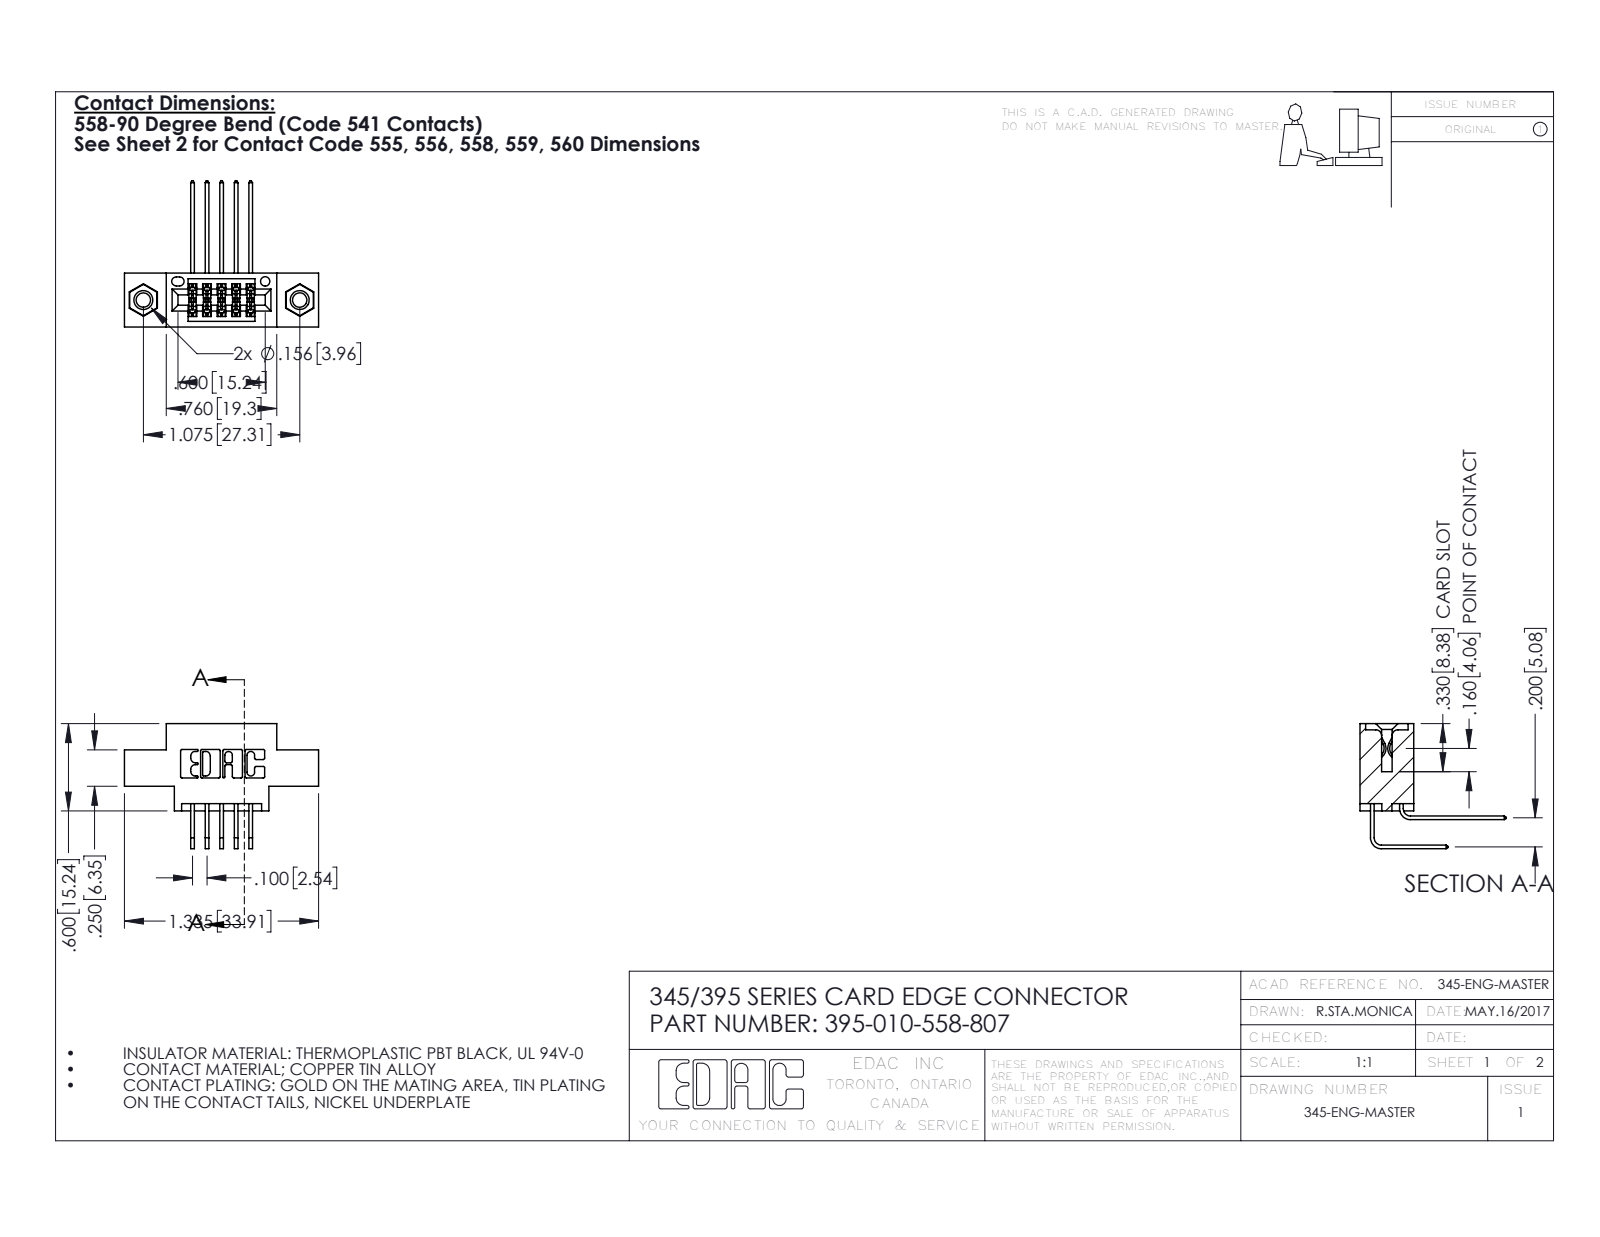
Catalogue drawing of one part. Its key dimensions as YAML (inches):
part_name: "345-292-001_558 559 Tail - 1; 345-292-001_558 Tail - 2; 345 Part_0.170 Offset - 0.156 Dia-TI; 345-250-001_345-250-005-103 (+1 more)"
step_written_by: "SolidWorks 2016 (CONFIG_CONTROL_DESIGN)"
units: inches
bodies: {solids: 13, faces: 710, planar: 466, cylindrical: 228, other: 16}
overall_size: [1.335, 1.005, 0.859]
volume: 0.176
surface_area: 6.177
round_holes:
  - {diameter: 0.098, count: 2}
  - {diameter: 0.125, count: 2}
  - {diameter: 0.156, count: 2}
  - {diameter: 0.064, count: 1}
round_bosses_or_shafts:
  - {diameter: 0.155, count: 2}
partial_cylinders:
  - {radius: 0.01, count: 22}
  - {radius: 0.006, count: 16}
  - {radius: 0.007, count: 6}
  - {radius: 0.031, count: 6}
  - {radius: 0.026, count: 3}
  - {radius: 0.014, count: 2}
  - {radius: 0.019, count: 2}
  - {radius: 0.022, count: 2}
face_to_face_distances: [0.2, 0.37, 0.1, 0.072, 0.298, 0.098, 0.272, 0.025, 0.25, 0.06]
hole_center_spacings: [0.27, 0.847, 1.075]
